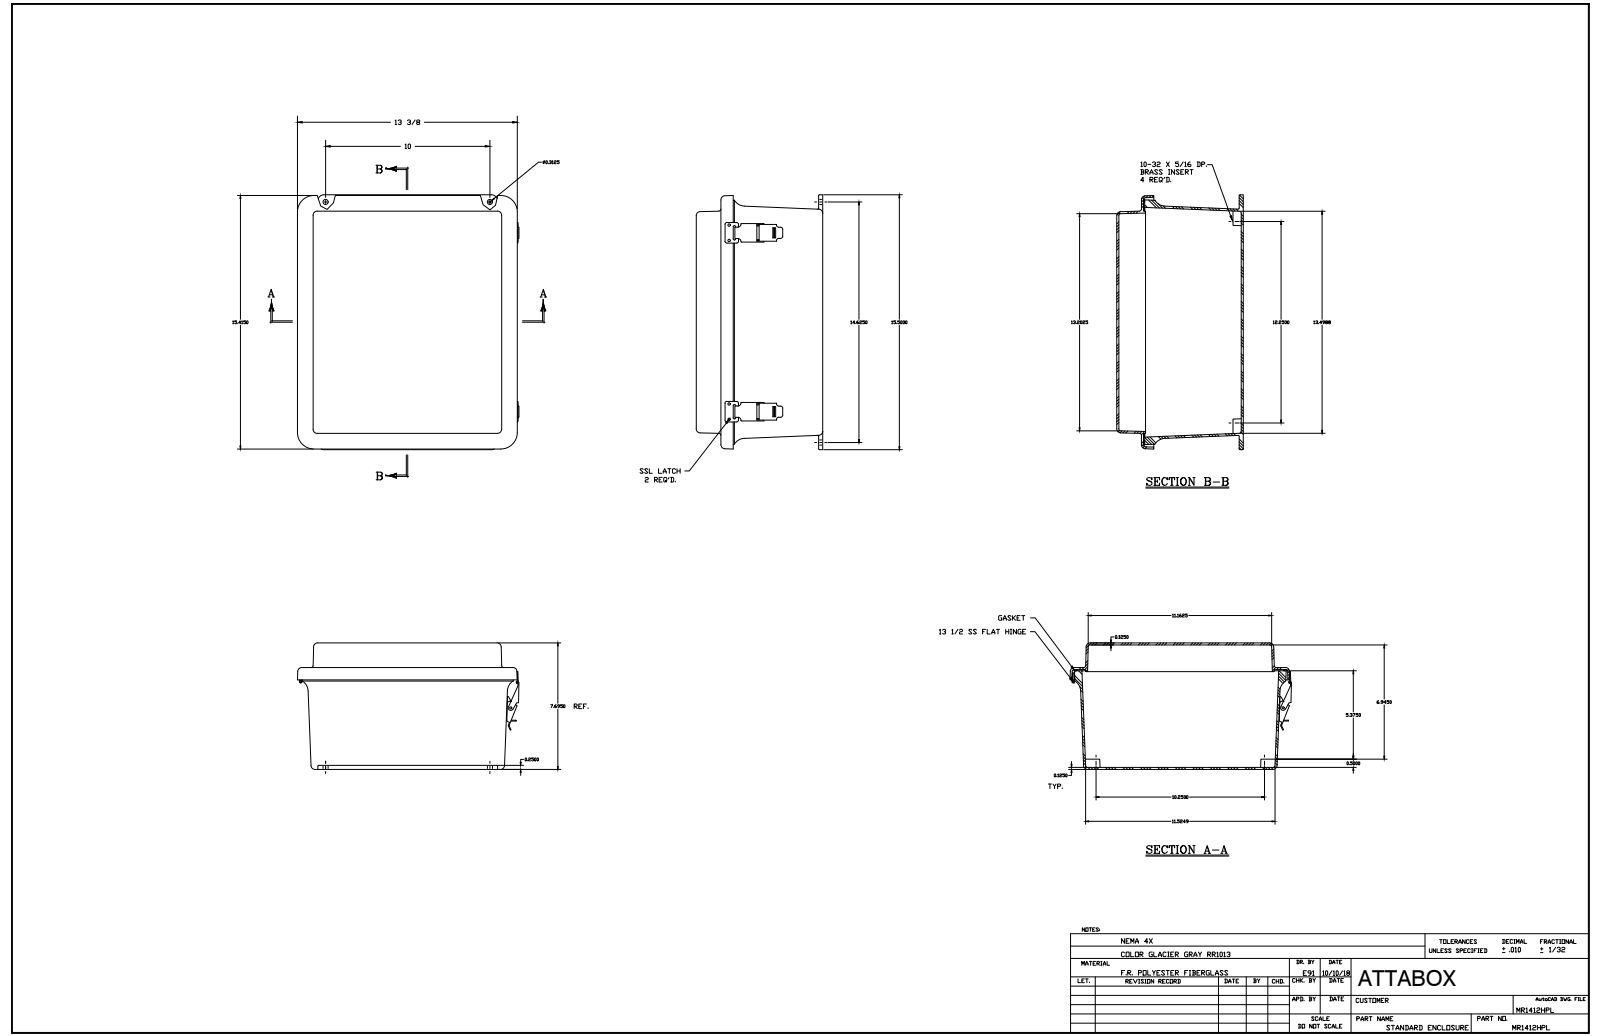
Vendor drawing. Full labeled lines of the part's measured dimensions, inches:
Part name (STEP PRODUCT): MR1412HPL
STEP written by: SolidWorks 2018 (AUTOMOTIVE_DESIGN)
Units: inches
Bodies: 38 solids, 1101 faces (474 planar, 456 cylindrical, 171 other)
Overall size (bounding box): 15.5 × 13.522 × 7.703
Volume: 119.5 in³ · Surface area: 1 743 in²
Round holes (diameter × count): ⌀0.14 ×22, ⌀0.131 ×10, ⌀0.104 ×8, ⌀0.152 ×8, ⌀0.13 ×4, ⌀0.156 ×4, ⌀0.218 ×4, ⌀0.135 ×2, ⌀0.375 ×2, ⌀0.085 ×1, ⌀0.085 ×1, ⌀0.135 ×1
Round bosses / shafts (diameter × count): ⌀0.125 ×10, ⌀0.25 ×8, ⌀0.125 ×6, ⌀0.27 ×4, ⌀0.3 ×1, ⌀0.17 ×1, ⌀0.155 ×1, ⌀0.155 ×1
Partial cylindrical surfaces — rounded edges, fillets, slot ends (radius × count): R0.125 ×28, R0.015 ×20, R0.031 ×20, R0.25 ×20, R0.045 ×16, R0.03 ×12, R0.023 ×8, R0.06 ×6
Main face-to-face distances: 0.125, 0.125, 7.453, 7.578, 7.703, 7.578, 1.5, 5.953, 6.078, 1.625
Hole centre spacings: 3.25, 6.5, 10.882, 0.25, 9.75, 10.881, 10.908, 3
